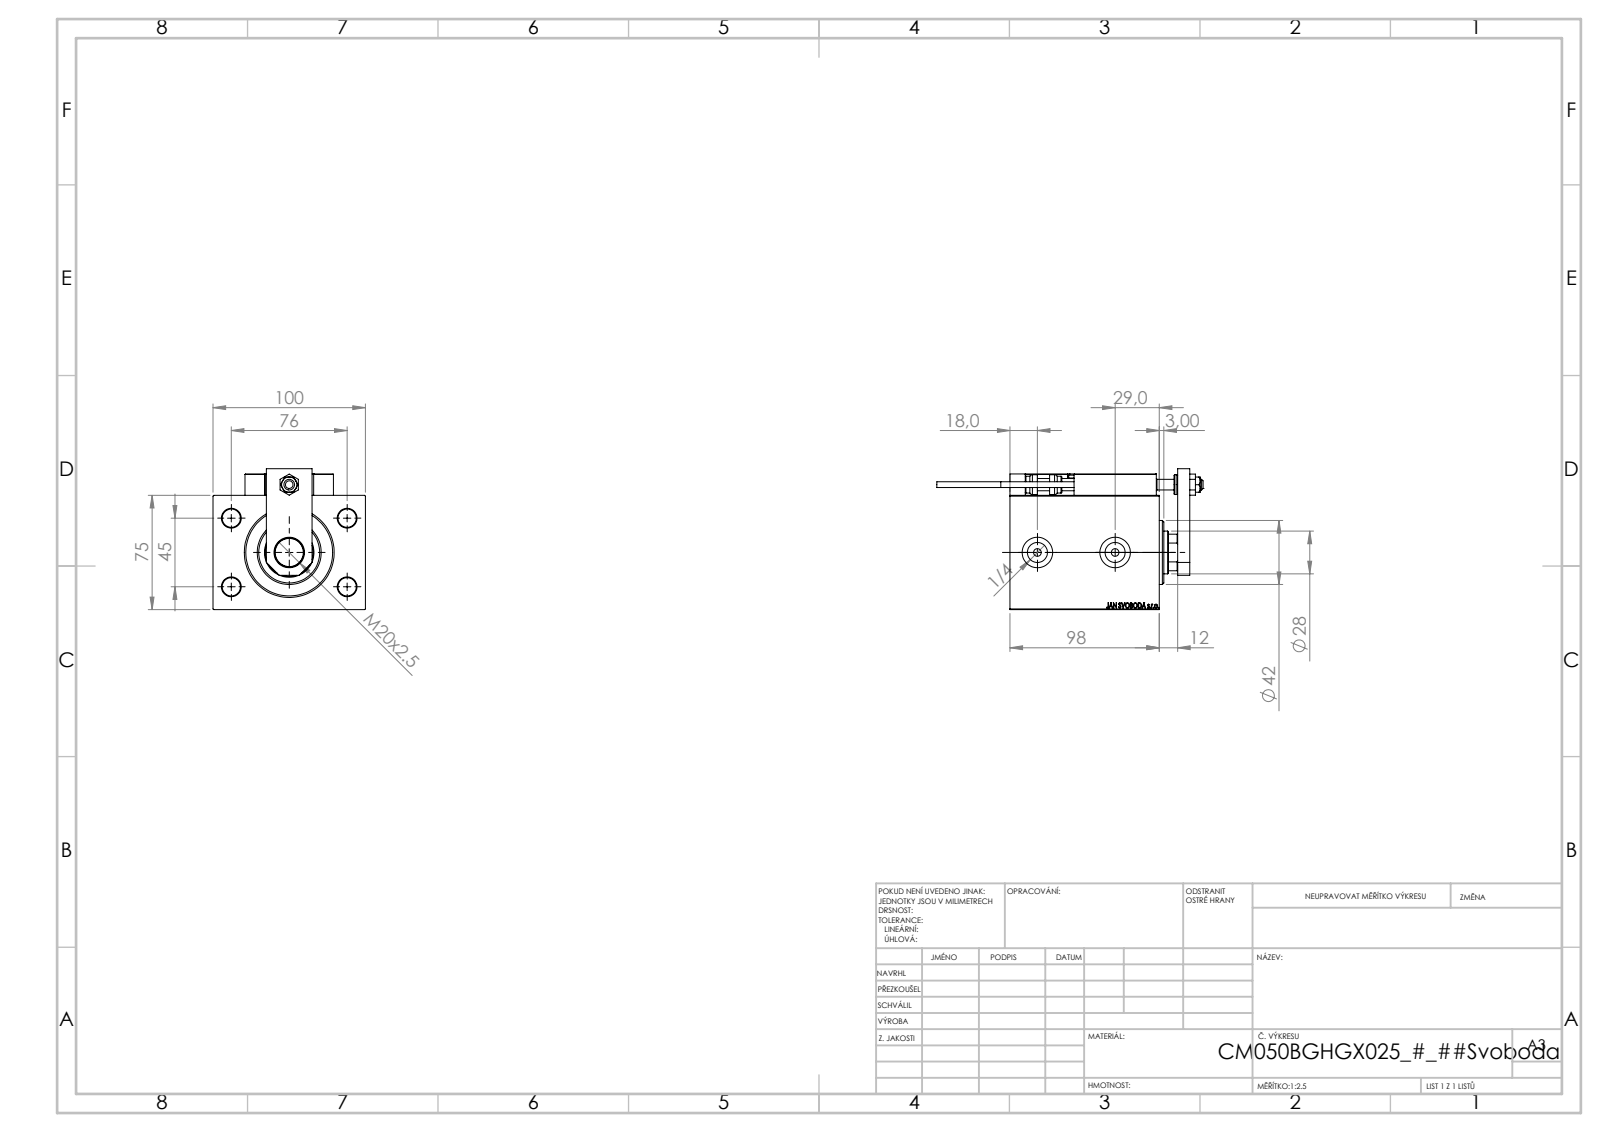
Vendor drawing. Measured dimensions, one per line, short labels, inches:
name: ZARAZKA; ALLEN BOLT D5; V450CM_VC_B; ALLEN BOLT D8 (+7 more)
written by: SolidWorks 2019 (CONFIG_CONTROL_DESIGN)
unit: in
bodies: 24 solids, 1321 faces (562 planar, 186 cylindrical, 573 other)
size: 6.878 × 3.937 × 3.642
volume: 44.86 in³; area: 188.5 in²
holes: 5× ⌀0.315, 4× ⌀0.126, 4× ⌀0.157, 4× ⌀0.197, 4× ⌀0.472, 3× ⌀0.787, 2× ⌀0.518, 1× ⌀0.276, 1× ⌀0.728, 1× ⌀1.102, 1× ⌀1.24, 1× ⌀1.28
bosses: 2× ⌀0.197, 2× ⌀0.15, 1× ⌀1.654, 1× ⌀0.512, 1× ⌀0.433
rounds: 30× R0.012, 2× R0.118, 1× R0.531
face distances: 2.953, 0.551, 3.937, 3.858, 0.472, 3.307, 1.26, 0.984, 0.945, 3.386
hole spacings: 1.739, 0.448, 0.787, 1.165, 1.169, 1.42, 1.661, 1.729
